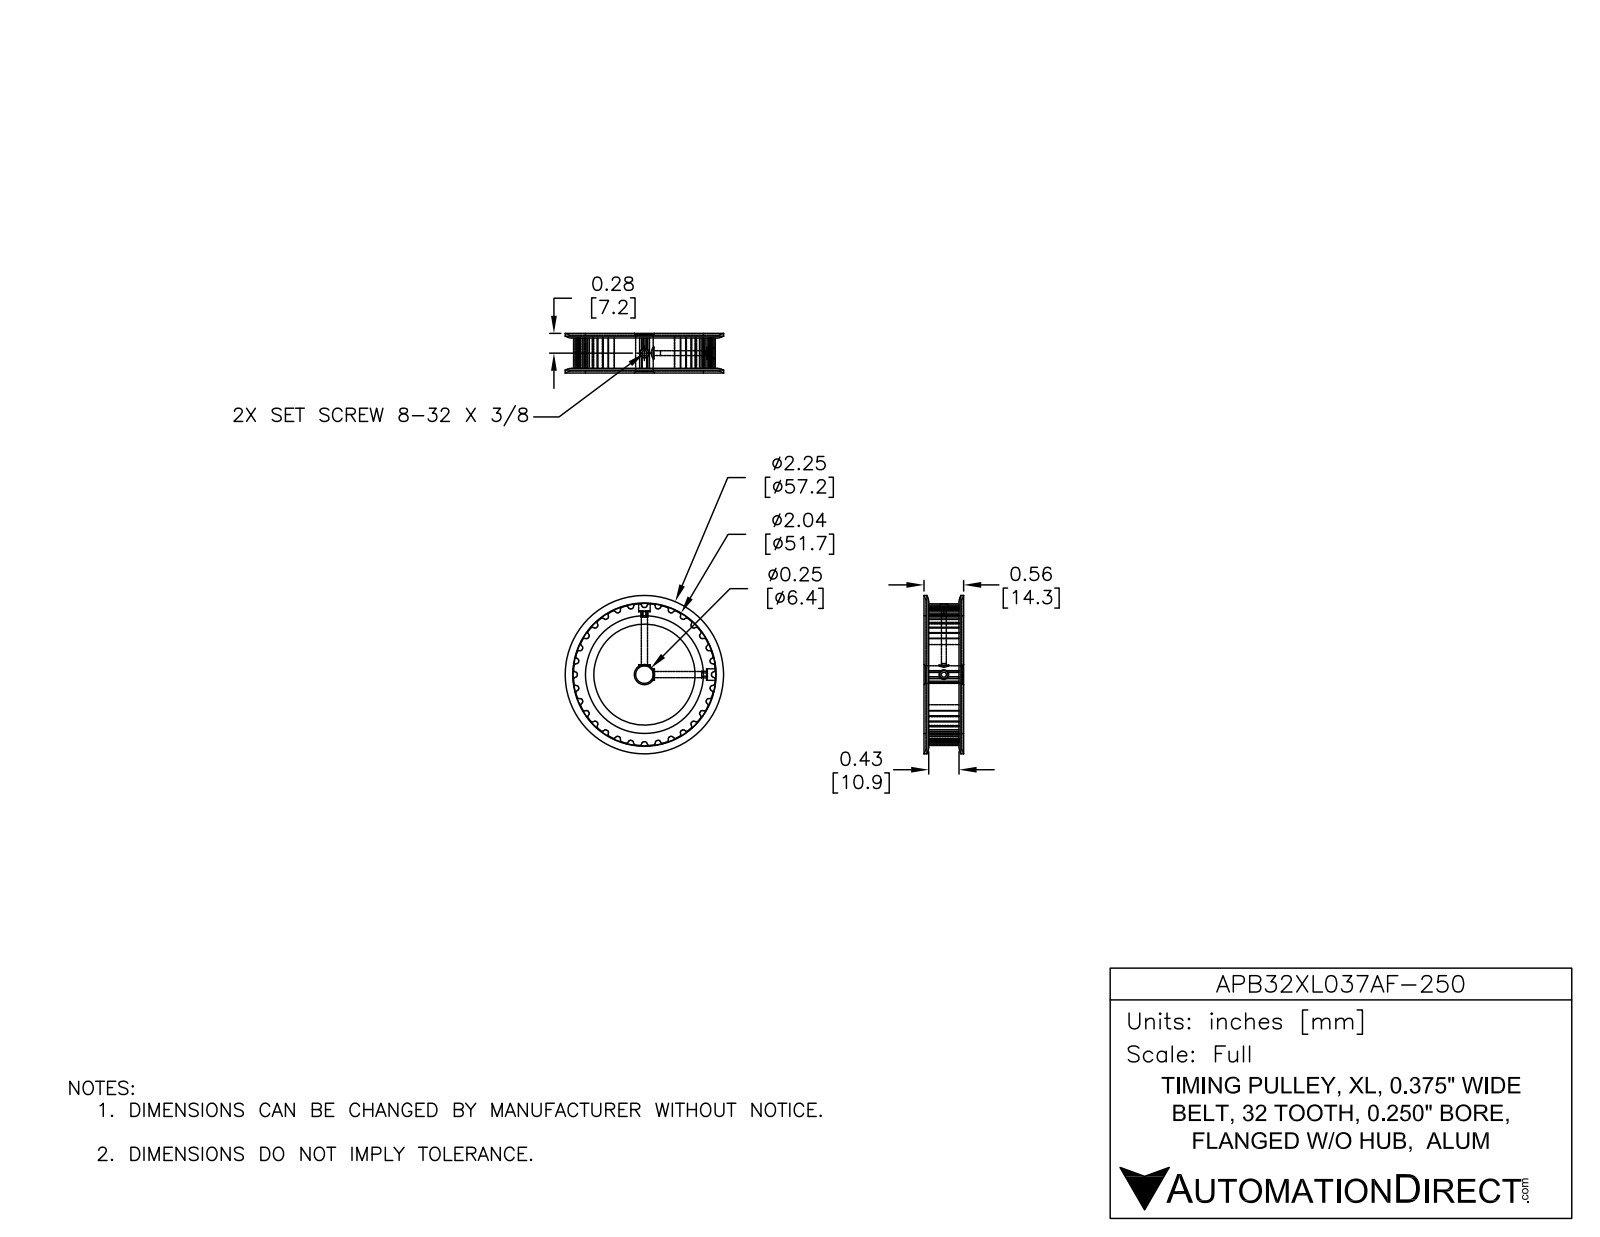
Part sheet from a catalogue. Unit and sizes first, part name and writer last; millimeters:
Units: millimetres
Overall size (bounding box): 57.2 × 57.2 × 14.1
Round holes (diameter × count): ⌀3.2 ×2, ⌀6.4 ×1
Round bosses / shafts (diameter × count): ⌀36.5 ×1
Partial cylindrical surfaces — rounded edges, fillets, slot ends (radius × count): R0.4 ×128, R24.2 ×1
Main face-to-face distances: 12.6, 0.8, 13.4, 14.1, 13.3, 0.8, 51.2, 19.3, 11.7, 1.6
Volume: 26 660 mm³ · Surface area: 9 664 mm²
Bodies: 1 solid, 326 faces (108 planar, 194 cylindrical, 24 other)
Part name (STEP PRODUCT): APB32XL037AF-250
STEP written by: SolidWorks 2014 (AUTOMOTIVE_DESIGN)
